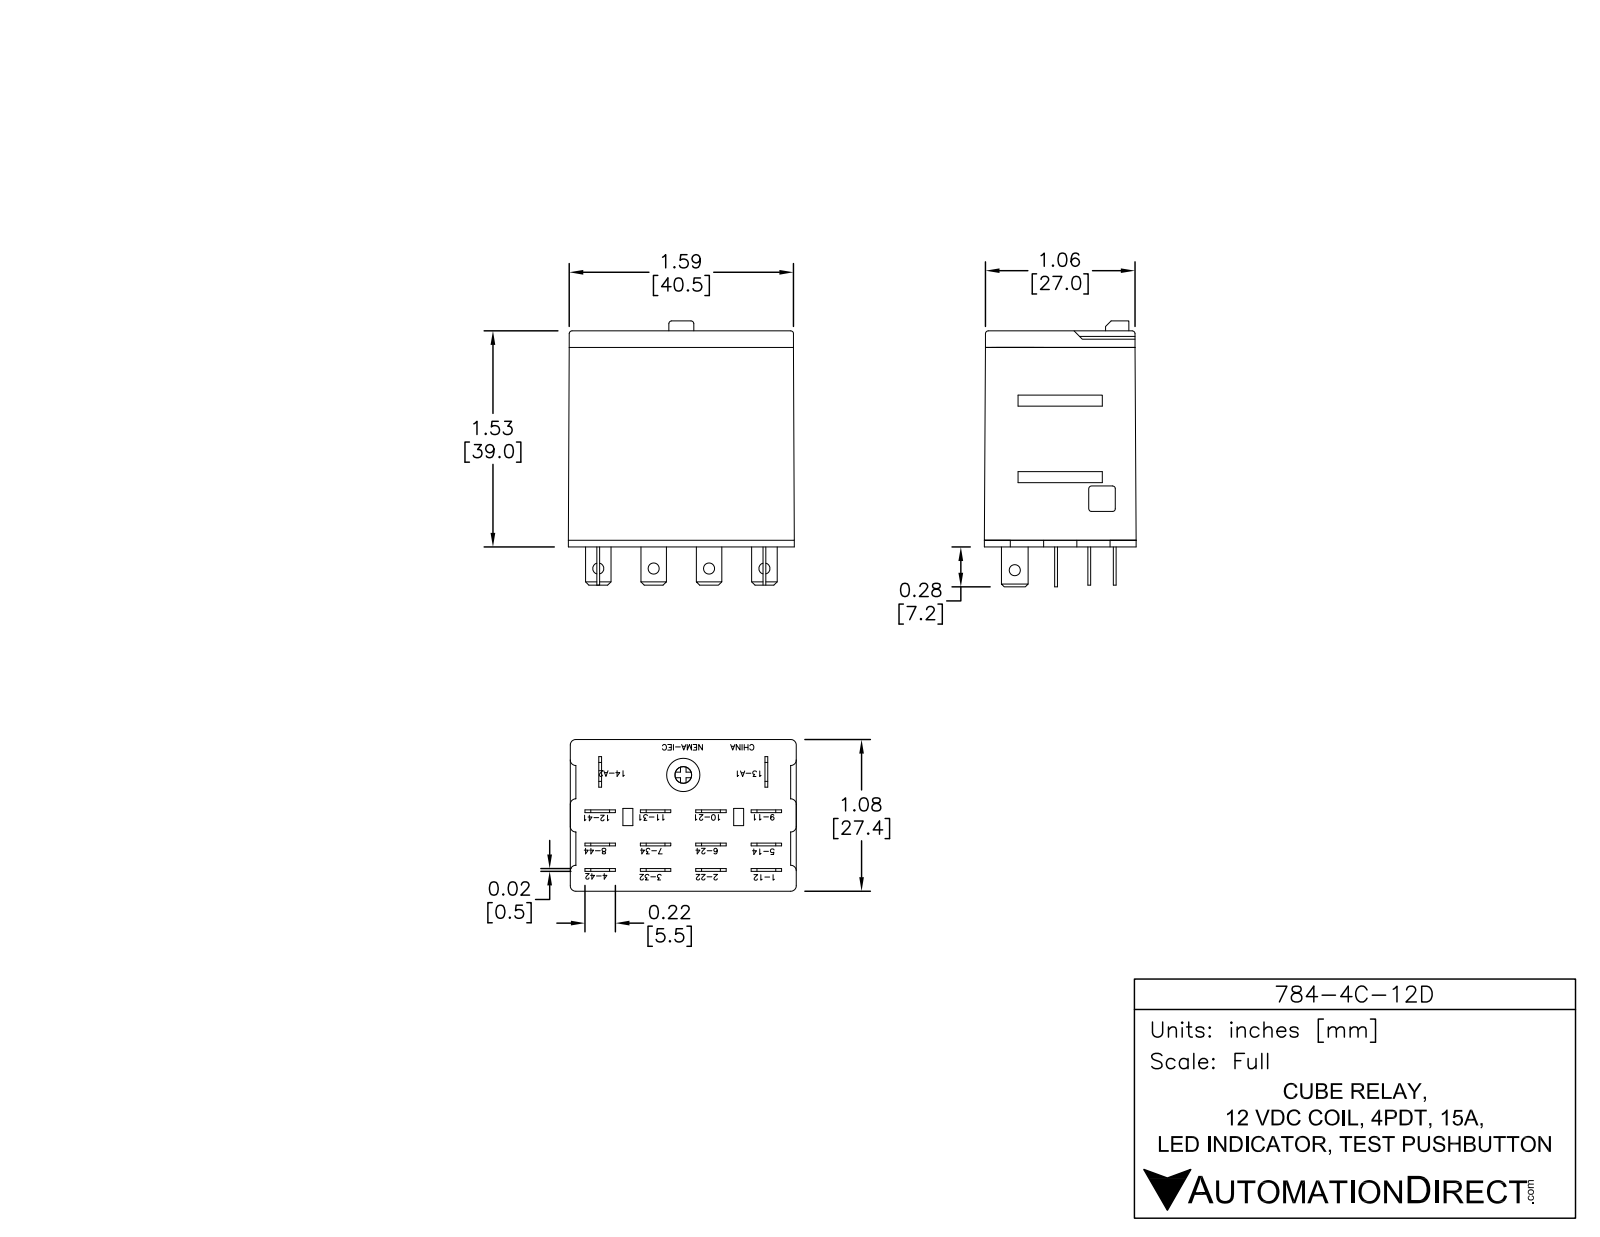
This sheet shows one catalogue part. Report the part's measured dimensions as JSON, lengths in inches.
{"part_name": "784-4C-12D", "step_written_by": "SolidWorks 2021 (CONFIG_CONTROL_DESIGN)", "units": "inches", "bodies": {"solids": 2, "faces": 227, "planar": 194, "cylindrical": 33, "other": 0}, "overall_size": [1.8, 1.6, 1.1], "volume_in3": 2.64, "surface_area_in2": 13.28, "round_holes": [[0.11, 5], [0.14, 1]], "round_bosses_or_shafts": [[0.07, 1]], "partial_cylinders_radius": [[0.28, 1]], "face_to_face_distances": [1.54, 0.02, 0.04, 0.21, 1.5, 0.23, 0.02, 0.03, 1.53, 0.25], "hole_center_spacings": [0.39, 0.78, 0.39, 1.17]}
